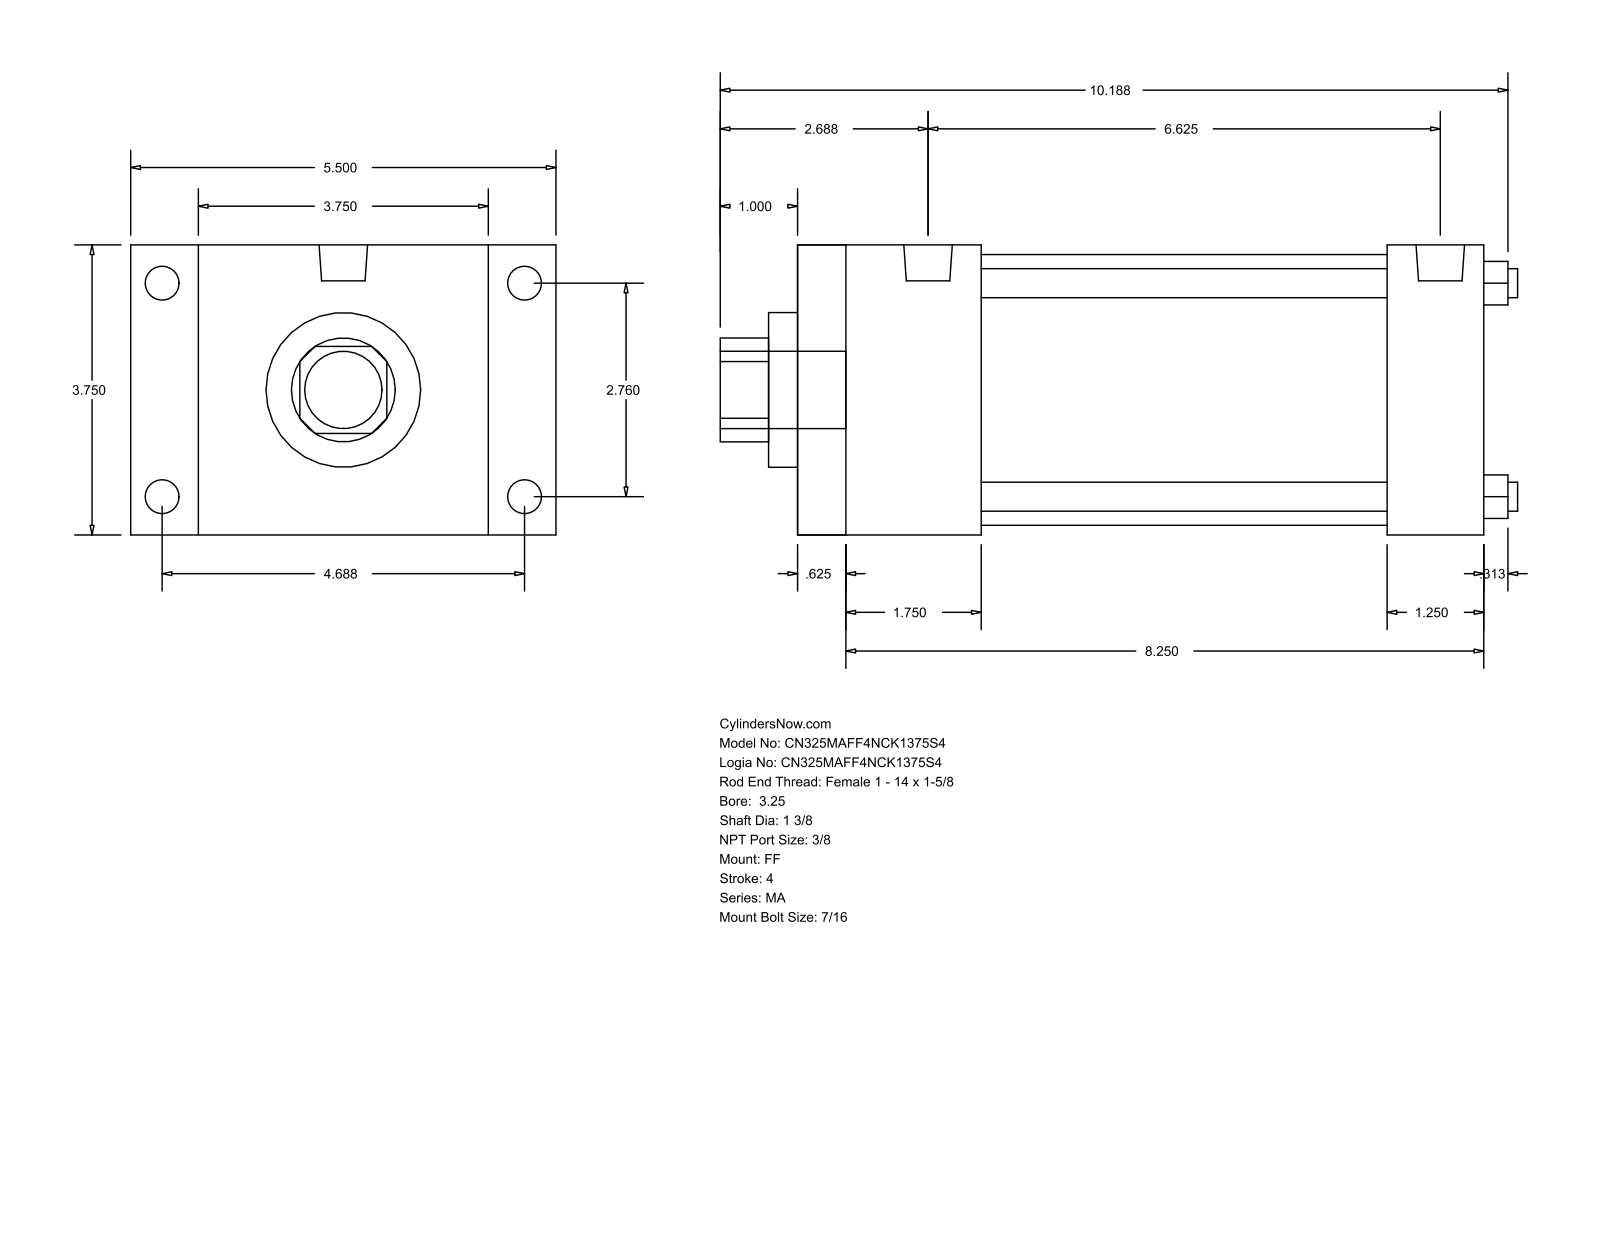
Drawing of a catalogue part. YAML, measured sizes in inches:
part_name: "MA_FF__0325_1.375"
step_written_by: "GSSL Pune (CONFIG_CONTROL_DESIGN)"
units: inches
bodies: {solids: 0, faces: 92, planar: 64, cylindrical: 28, other: 0}
overall_size: [10.313, 5.5, 3.75]
round_holes:
  - {diameter: 0.375, count: 4}
  - {diameter: 1.375, count: 1}
  - {diameter: 2, count: 1}
  - {diameter: 3.5, count: 1}
round_bosses_or_shafts:
  - {diameter: 0.437, count: 8}
  - {diameter: 0.627, count: 2}
  - {diameter: 1, count: 1}
partial_cylinders:
  - {radius: 0.672, count: 1}
face_to_face_distances: [3.75, 8.875, 0.625, 8.25, 0.875, 4.625, 2.375, 7.625, 1.75, 7]
hole_center_spacings: [1.952, 2.76, 3.903]
